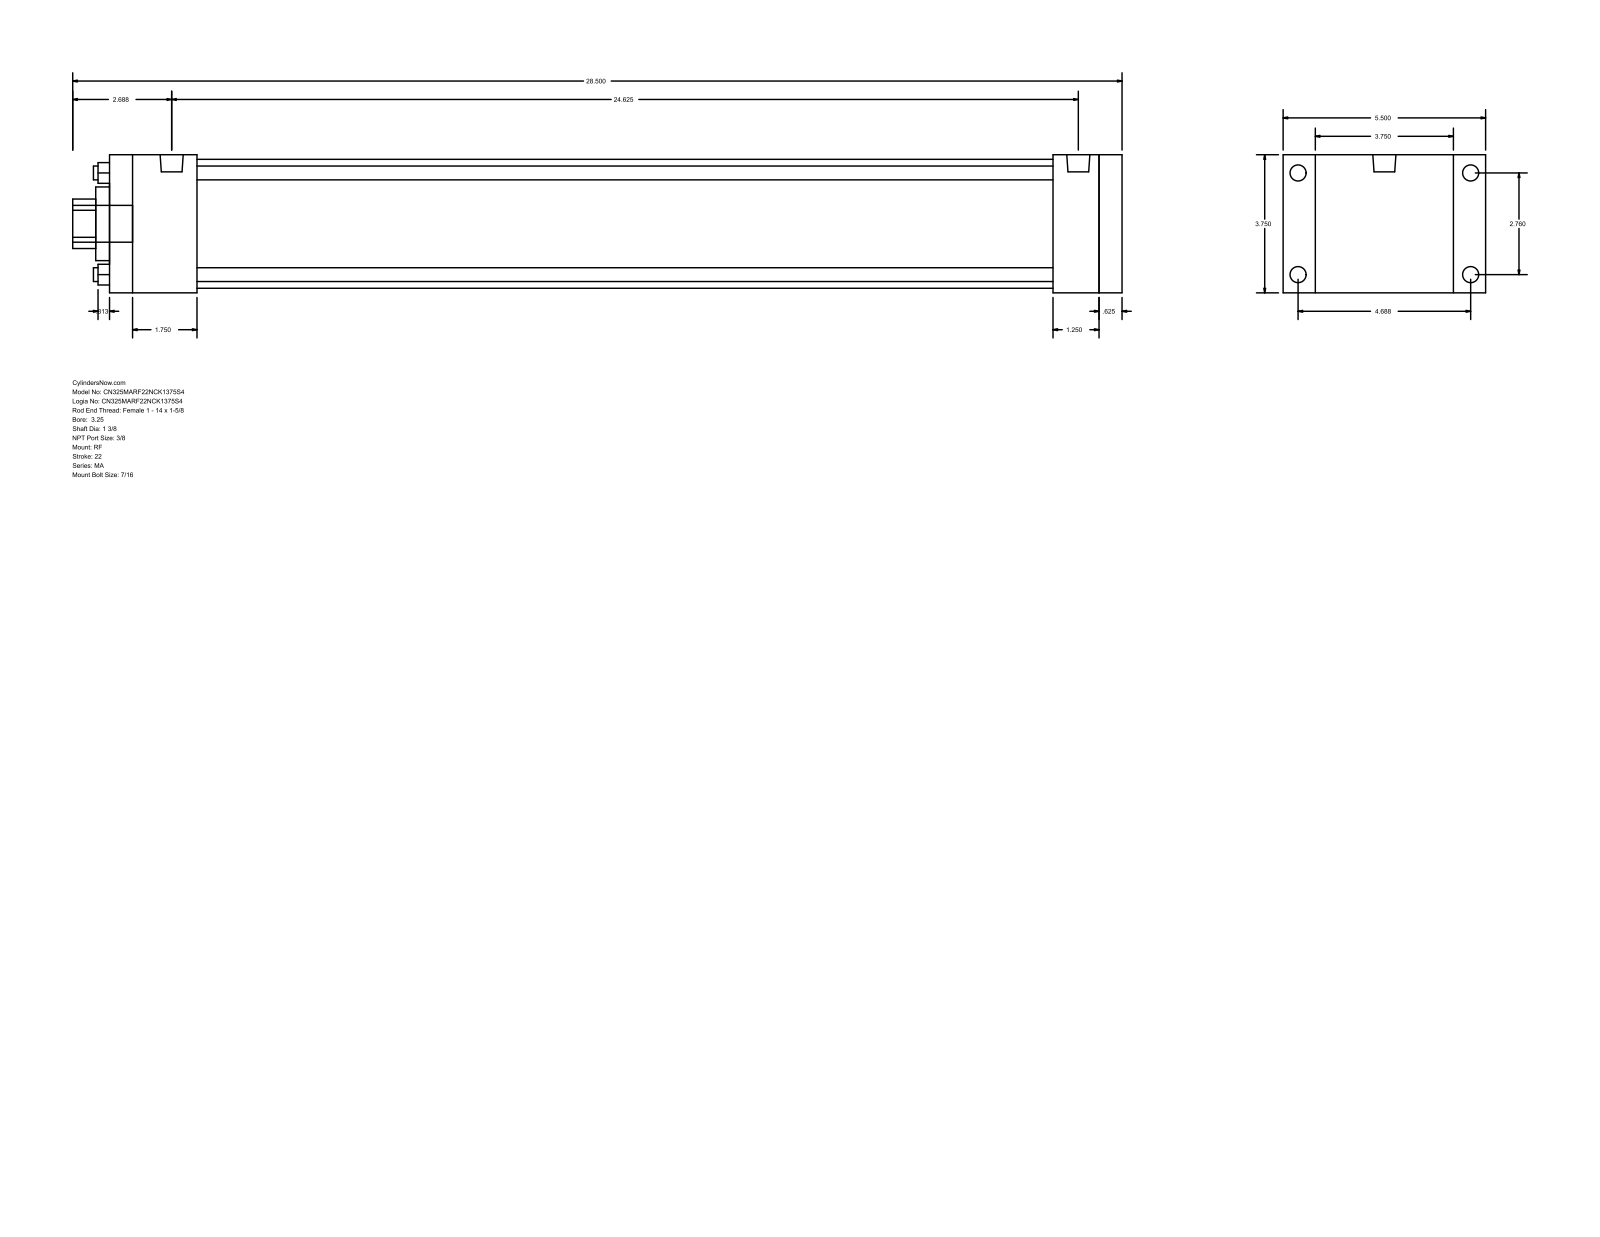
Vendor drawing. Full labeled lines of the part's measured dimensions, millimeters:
Part name (STEP PRODUCT): MA_RF__0325_1.375
STEP written by: GSSL Pune (CONFIG_CONTROL_DESIGN)
Units: millimetres
Bodies: 0 solids, 92 faces (64 planar, 28 cylindrical, 0 other)
Overall size (bounding box): 723.9 × 139.7 × 95.25
Round holes (diameter × count): ⌀9.53 ×4, ⌀34.92 ×1, ⌀50.8 ×1, ⌀88.9 ×1
Round bosses / shafts (diameter × count): ⌀11.11 ×8, ⌀15.93 ×2, ⌀25.4 ×1
Partial cylindrical surfaces — rounded edges, fillets, slot ends (radius × count): R17.06 ×1
Main face-to-face distances: 95.24, 698.5, 15.88, 682.62, 22.23, 117.47, 650.87, 31.75, 47.63, 60.32
Hole centre spacings: 49.57, 70.1, 99.14
